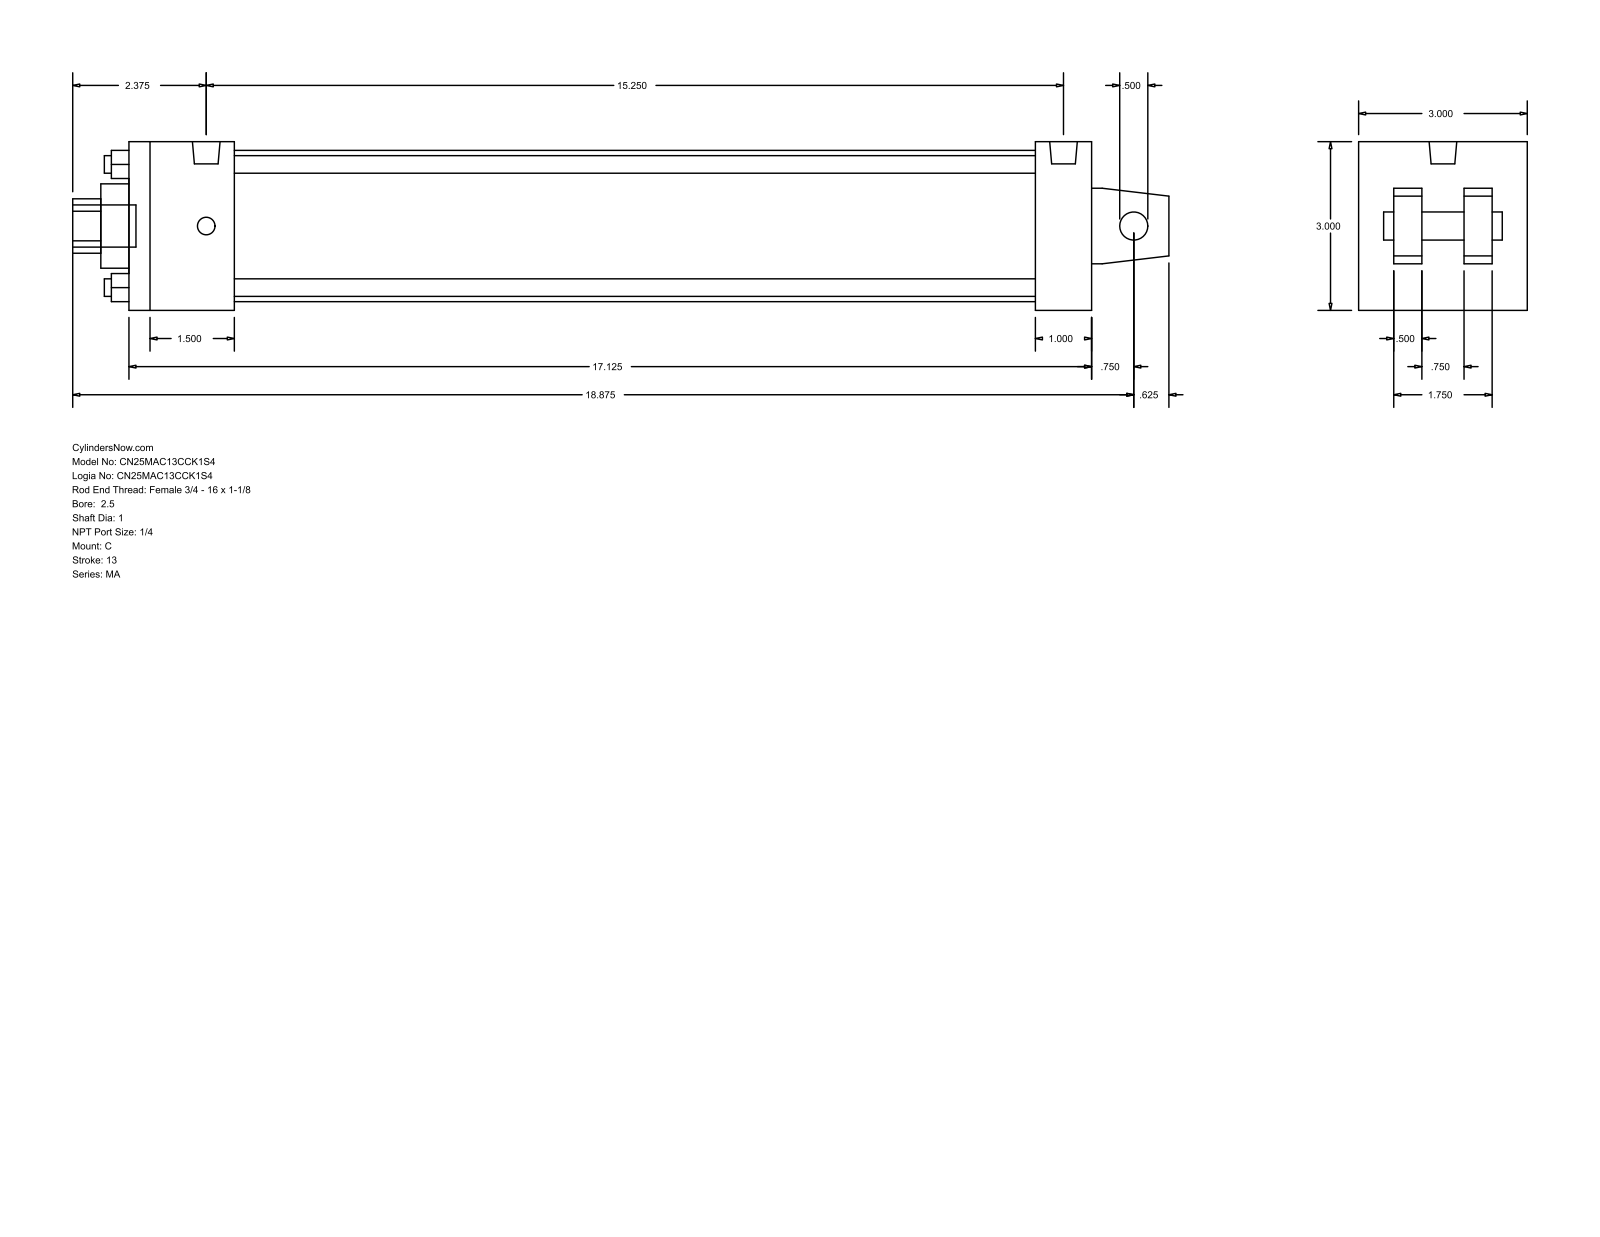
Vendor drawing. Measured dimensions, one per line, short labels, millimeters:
name: MA_C__0250_1
written by: GSSL Pune (CONFIG_CONTROL_DESIGN)
unit: mm
bodies: 0 solids, 103 faces (76 planar, 27 cylindrical, 0 other)
size: 495.3 × 76.2 × 76.2
holes: 4× ⌀7.94, 1× ⌀12.7, 1× ⌀25.4, 1× ⌀38.1, 1× ⌀68.33
bosses: 4× ⌀7.94, 2× ⌀12.49, 1× ⌀19.05
rounds: 1× R12.29
face distances: 76.2, 434.98, 47.63, 12.7, 15.87, 60.33, 25.4, 28.57, 409.58, 361.95
hole spacings: 39.33, 55.62, 78.66
